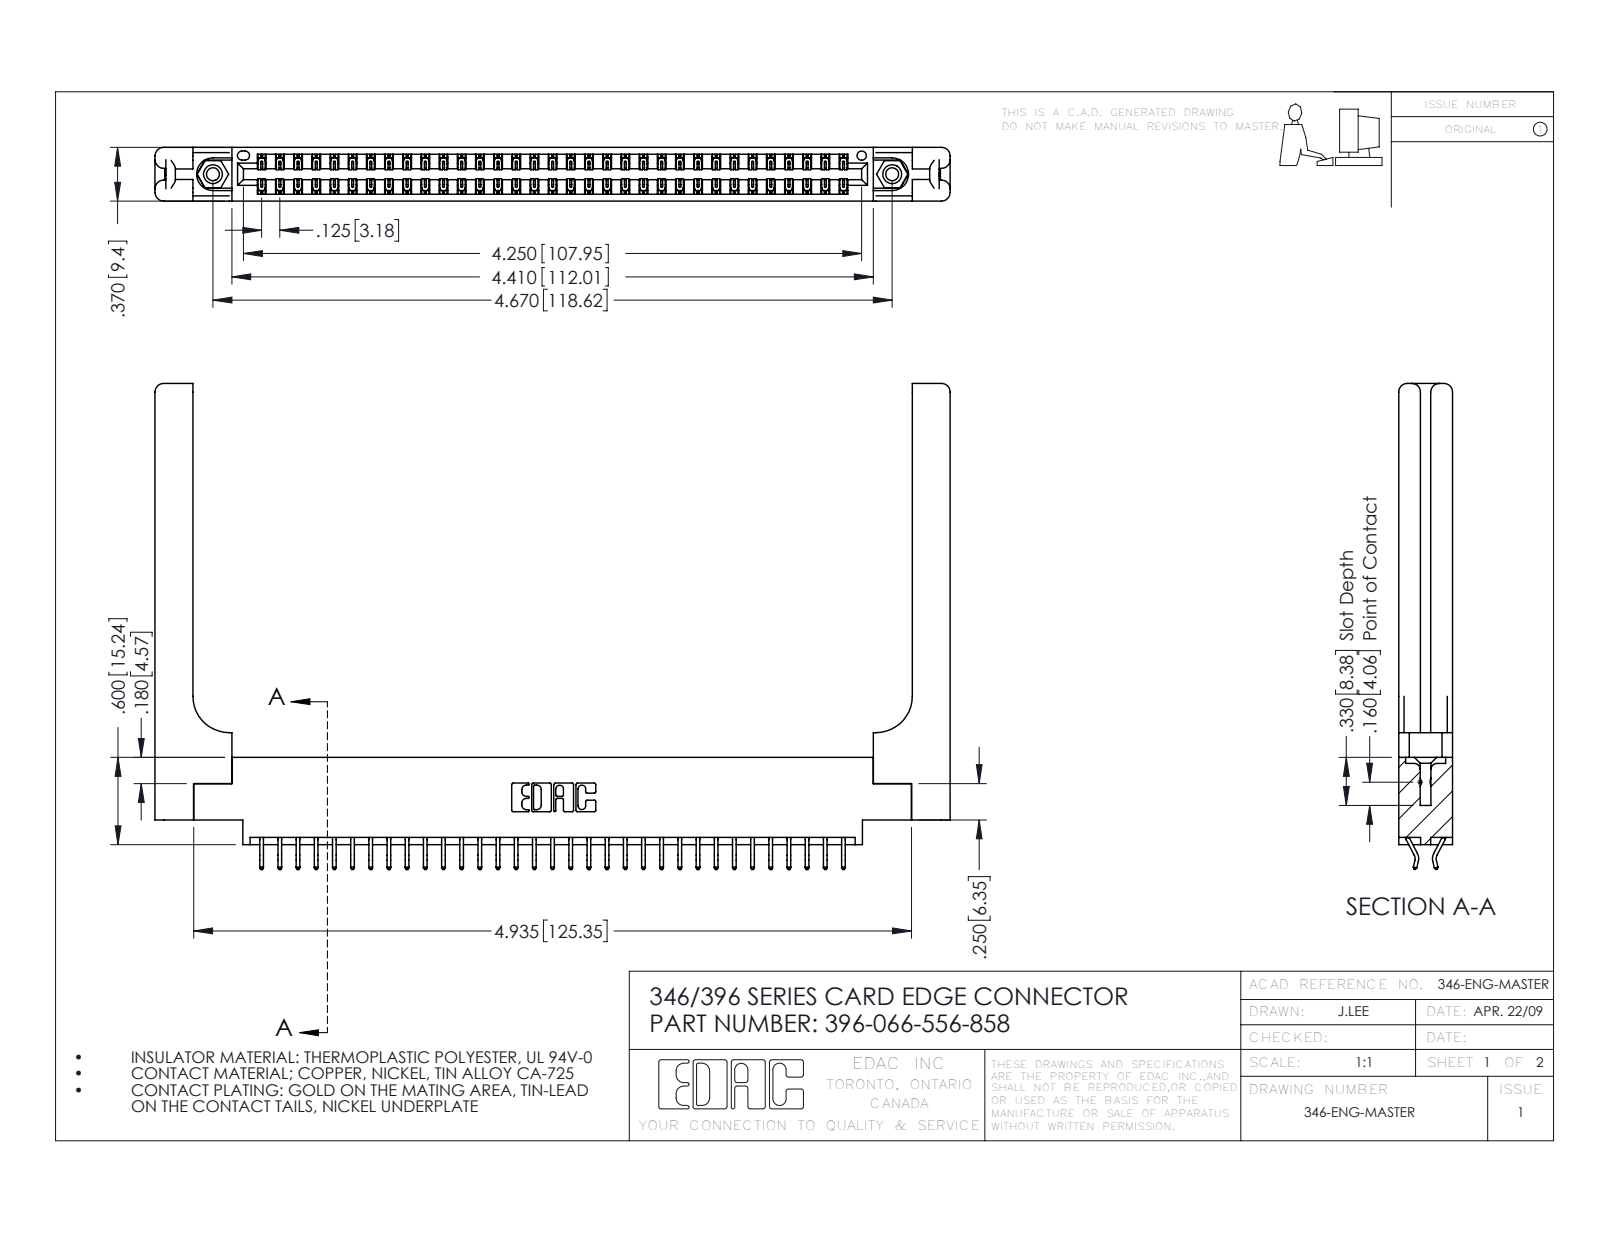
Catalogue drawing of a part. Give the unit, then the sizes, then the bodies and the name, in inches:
Units: inches
Overall size (bounding box): 5.466 × 3.34 × 0.37
Round holes (diameter × count): ⌀0.089 ×2, ⌀0.125 ×2, ⌀0.156 ×2, ⌀0.064 ×1
Round bosses / shafts (diameter × count): ⌀0.155 ×2
Partial cylindrical surfaces — rounded edges, fillets, slot ends (radius × count): R0.006 ×99, R0.01 ×22, R0.06 ×16, R0.007 ×6, R0.031 ×6, R0.026 ×3, R0.01 ×2, R0.014 ×2
Main face-to-face distances: 0.37, 0.048, 0.322, 0.072, 0.148, 0.15, 0.25, 0.025, 0.298, 0.275
Hole centre spacings: 0.246, 4.462, 4.67
Volume: 1.27 in³ · Surface area: 36.03 in²
Bodies: 71 solids, 4210 faces (2802 planar, 1348 cylindrical, 60 other)
Part name (STEP PRODUCT): 396-066-556-858; 345-292-001_556 Tail; 346-220-058_345-220-058; 346 Part_0.170 Offset - 0.156 Dia-TH (+1 more)
STEP written by: SolidWorks 2016 (CONFIG_CONTROL_DESIGN)
